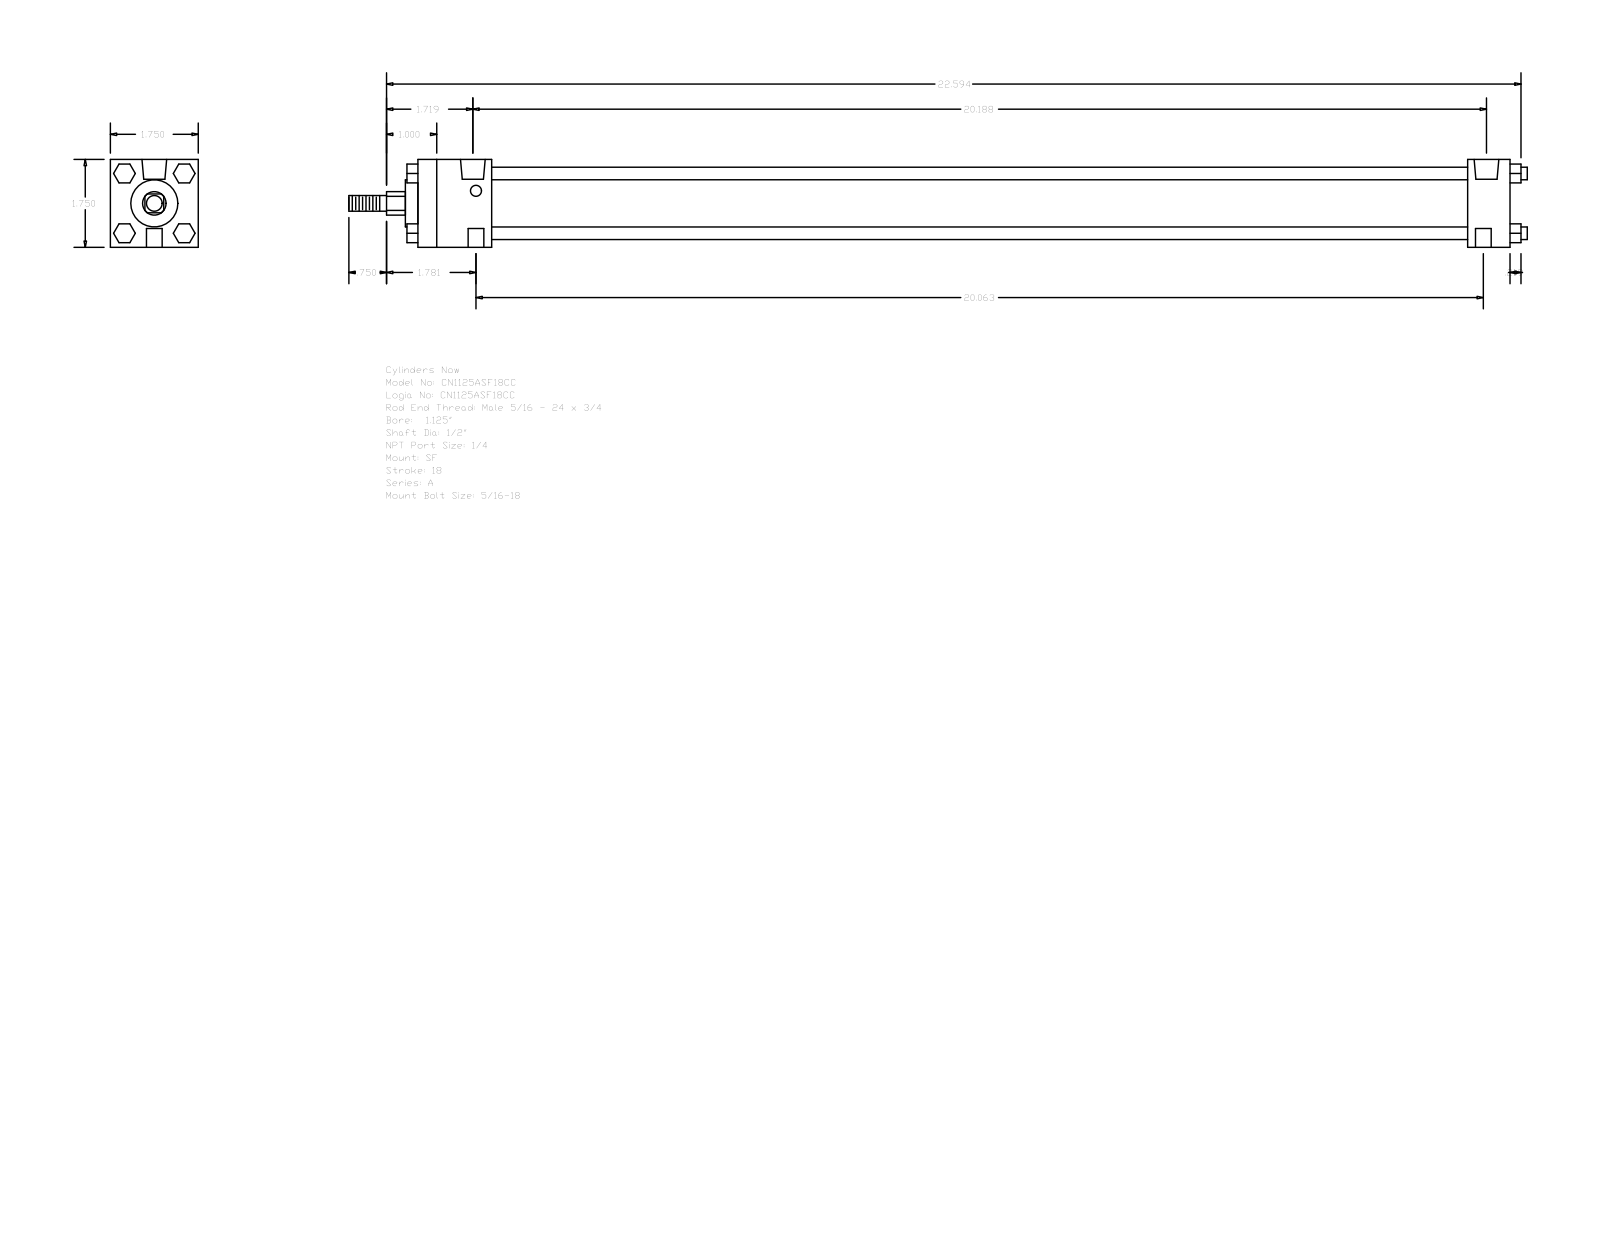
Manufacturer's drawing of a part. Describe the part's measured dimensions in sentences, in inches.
The part is named "A_SF__0112_0.5". Its 3-D file was written by "GSSL Pune (CONFIG_CONTROL_DESIGN)". It is 0 solids with 120 faces: 92 planar, 28 cylindrical and 0 other. Overall it measures 23.469 by 1.75 by 1.75 inches. Round holes: 2 of diameter 0.219, 2 of diameter 0.313, 2 of diameter 0.492. Round bosses or shafts: 4 of diameter 0.25, 1 of diameter 1.255, 1 of diameter 0.937, 1 of diameter 0.5, 1 of diameter 0.313. Partial cylindrical surfaces (rounded edges, fillets, slot ends): 1 of radius 0.234. The main face-to-face distances are 1.75, 21.75, 20.906, 0.844, 1.469, 19.437, 20.281, 0.375, 0.22, 1.063. The hole center spacings are 20.063, 0.062, 0.063, 20.125, 20.125, 20.187.
